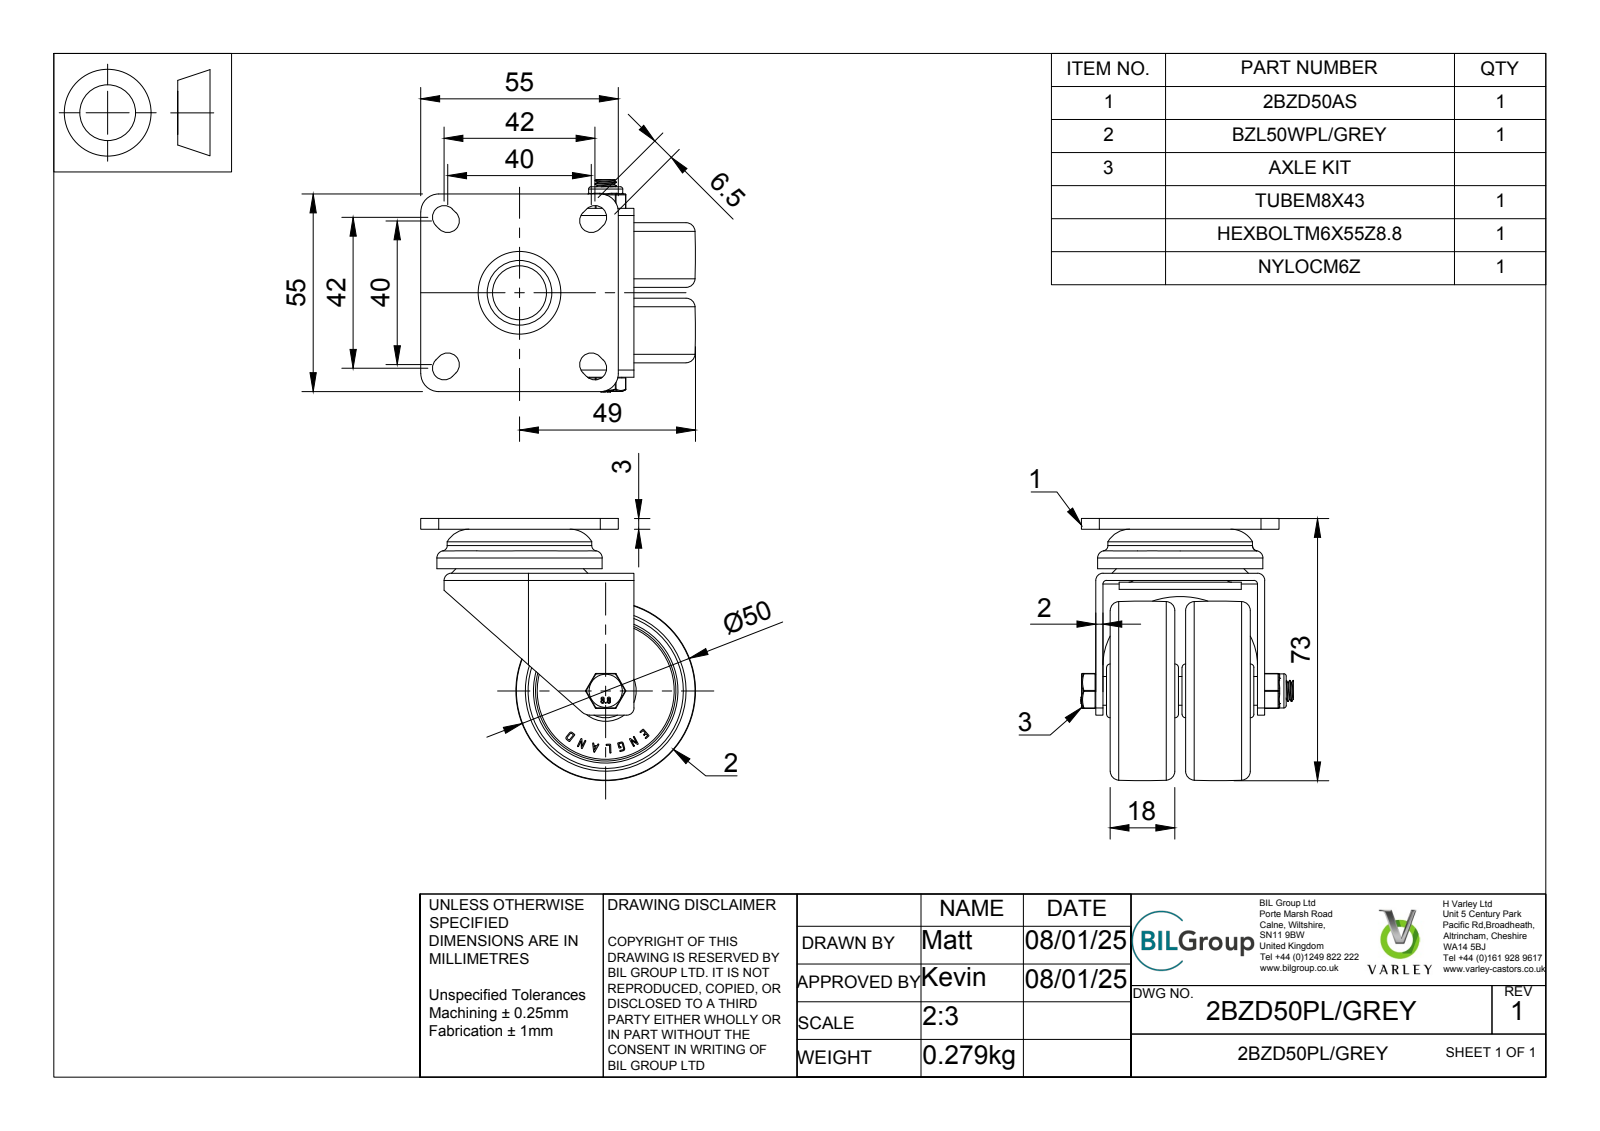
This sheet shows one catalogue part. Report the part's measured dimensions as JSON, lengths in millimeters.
{"part_name": "2BZD50PL/GREY v3; 2BZD50AS v1; ZINC PLATED PRESSED STEEL TOP PLATE; ZINC PLATED PRESSED STEEL FORKS (+8 more)", "step_written_by": "Autodesk Translation Framework v13.20.0.188 (AP242_MANAGED_MODEL_BASED_3D_ENGINEERING_MIM_LF)", "units": "millimeters", "bodies": {"solids": 8, "faces": 582, "planar": 269, "cylindrical": 119, "other": 194}, "overall_size": [76.5, 73, 59.15], "volume_mm3": 64968, "surface_area_mm2": 45034, "round_holes": [[6, 1], [6.2, 1], [7, 1], [8.1, 1], [30, 1], [36.25, 1], [42, 1]], "round_bosses_or_shafts": [[15, 2], [46, 1], [40.25, 1], [34, 1], [14, 1], [9.5, 1], [9, 1], [8, 1]], "partial_cylinders_radius": [[0.25, 14], [3.25, 8], [0.23, 4], [0.45, 4], [5, 4], [2, 3], [0.44, 2], [0.45, 2]], "face_to_face_distances": [3, 2, 21, 11.5, 9.5, 32.5, 12.5, 45, 35.5, 33.5]}
